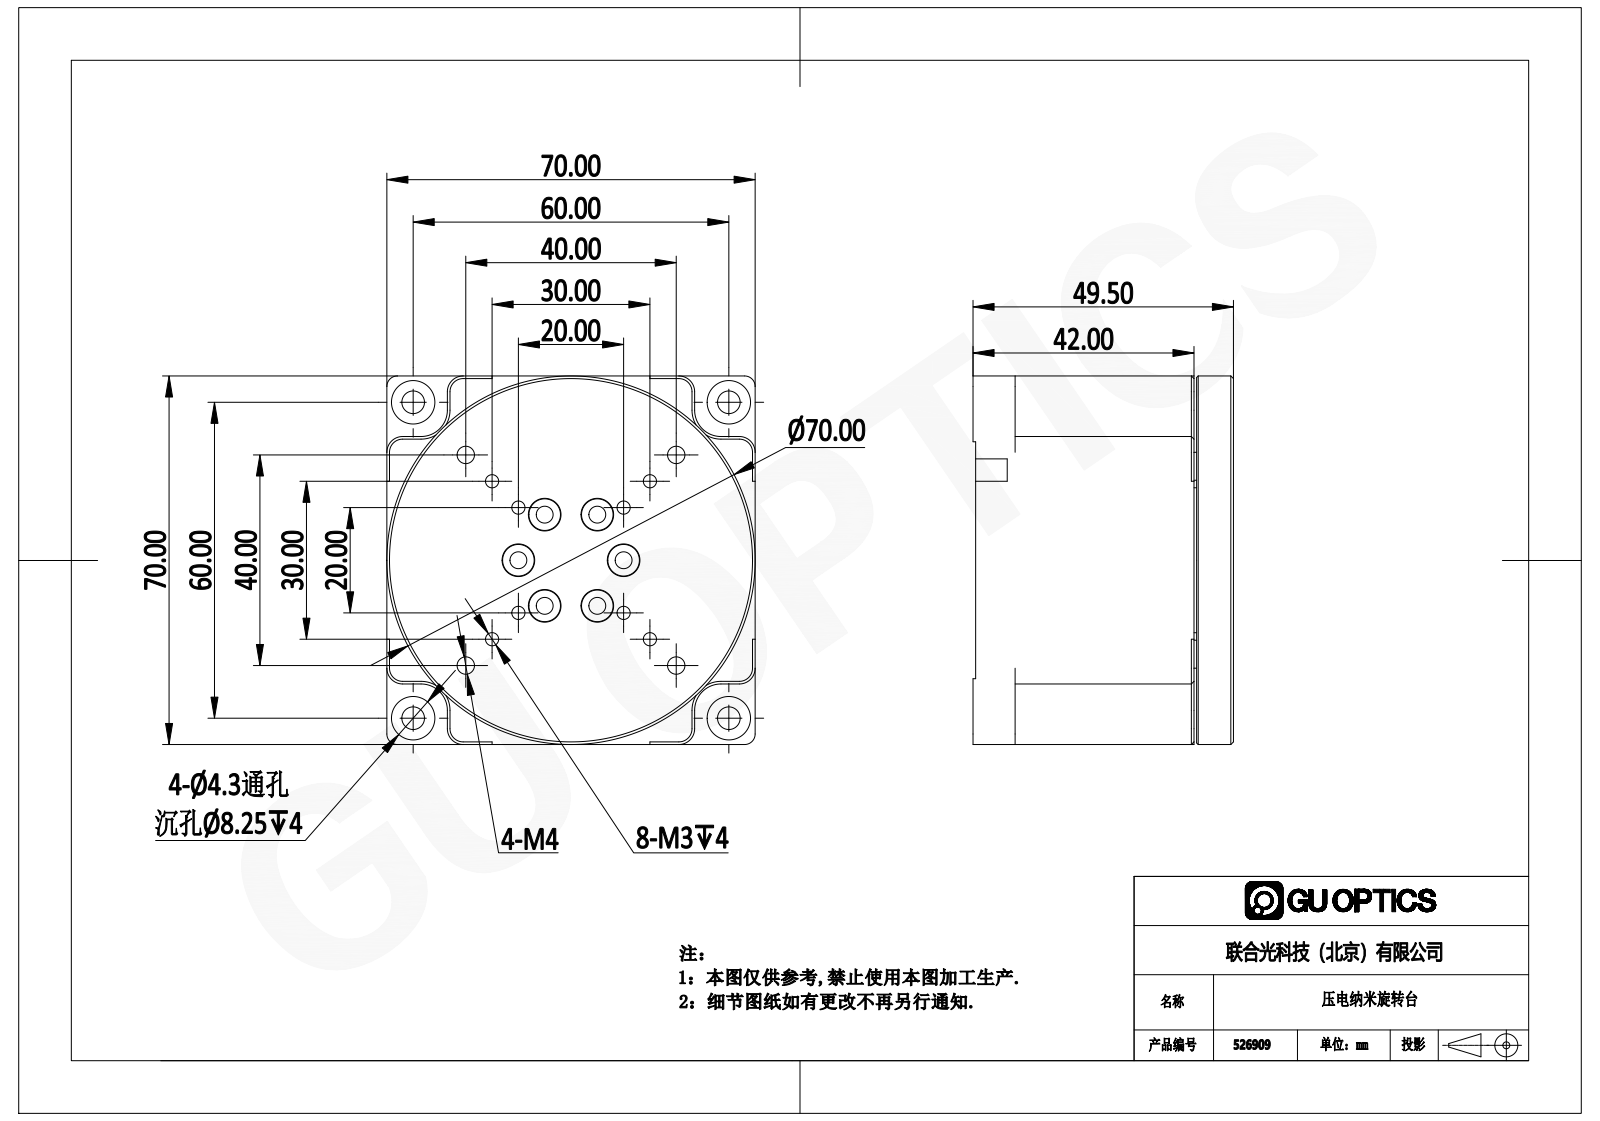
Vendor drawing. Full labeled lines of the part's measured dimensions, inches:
Part name (STEP PRODUCT): 526903
STEP written by: SolidWorks 2020 (CONFIG_CONTROL_DESIGN)
Units: inches
Bodies: 2 solids, 167 faces (83 planar, 63 cylindrical, 21 other)
Overall size (bounding box): 2.756 × 2.756 × 1.949
Volume: 12.98 in³ · Surface area: 49.54 in²
Round holes (diameter × count): ⌀0.098 ×8, ⌀0.126 ×6, ⌀0.244 ×6, ⌀0.13 ×4, ⌀0.169 ×4, ⌀0.325 ×4
Round bosses / shafts (diameter × count): ⌀2.756 ×1, ⌀1.614 ×1, ⌀0.472 ×1
Partial cylindrical surfaces — rounded edges, fillets, slot ends (radius × count): R0.118 ×12, R0.079 ×4, R0.197 ×4, R1.332 ×1
Main face-to-face distances: 1.634, 0.295, 2.756, 1.929, 0.02, 1.654, 0.276, 0.059, 0.039, 0.335
Hole centre spacings: 1.392, 0.394, 0.278, 0.557, 0.88, 1.004, 1.245, 1.42
